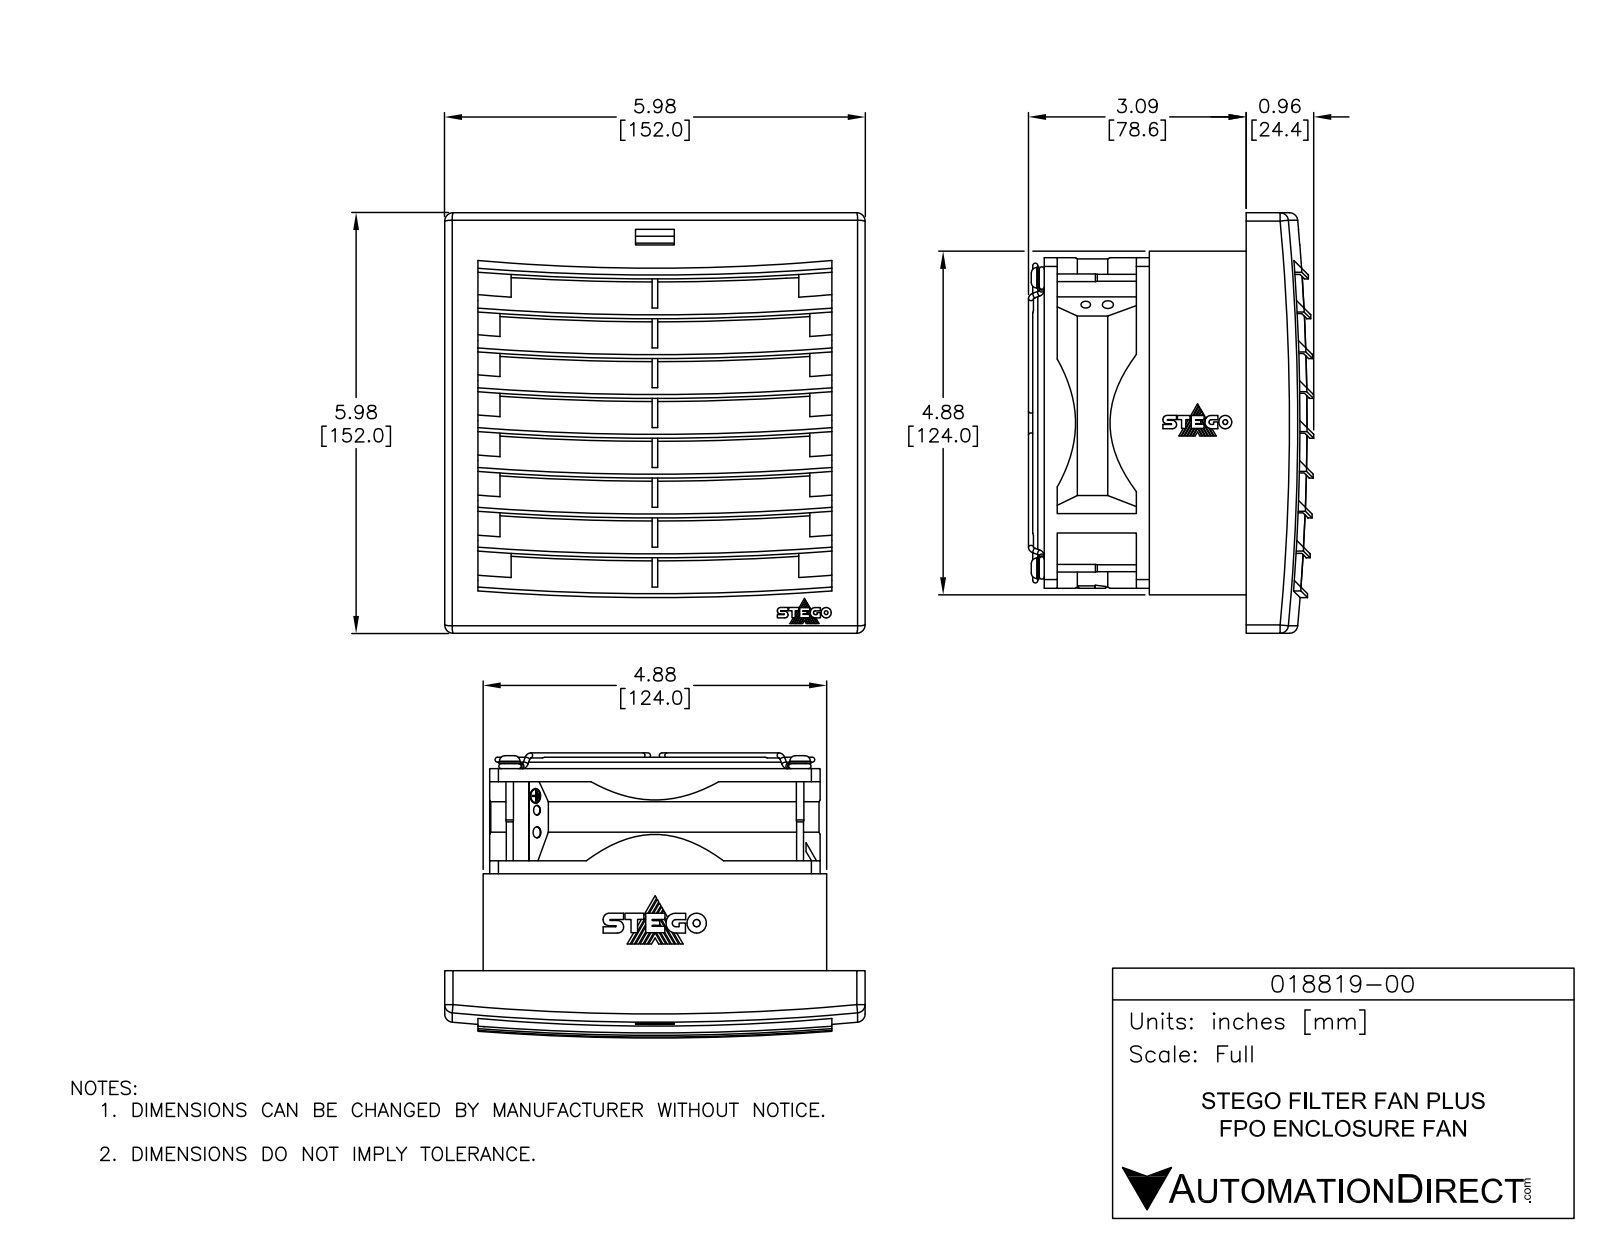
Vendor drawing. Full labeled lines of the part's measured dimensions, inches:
Part name (STEP PRODUCT): 018819-00
STEP written by: SolidWorks 2018 (AUTOMOTIVE_DESIGN)
Units: inches
Bodies: 1 solid, 544 faces (329 planar, 207 cylindrical, 8 other)
Overall size (bounding box): 5.985 × 5.984 × 4.094
Volume: 32.77 in³ · Surface area: 359.5 in²
Round holes (diameter × count): ⌀0.256 ×4, ⌀0.98 ×1, ⌀1.66 ×1, ⌀2.34 ×1, ⌀3.02 ×1, ⌀3.253 ×1, ⌀3.78 ×1, ⌀4.15 ×1
Round bosses / shafts (diameter × count): ⌀4.346 ×1, ⌀3.49 ×1, ⌀3.178 ×1, ⌀2.712 ×1, ⌀2.498 ×1, ⌀1.817 ×1, ⌀1.323 ×1, ⌀1.137 ×1
Partial cylindrical surfaces — rounded edges, fillets, slot ends (radius × count): R13.757 ×16, R1.852 ×5, R0.118 ×4, R0.142 ×4, R0.519 ×1, R0.849 ×1, R0.967 ×1, R1.238 ×1
Main face-to-face distances: 0.059, 0.426, 0.122, 4.76, 0.852, 0.079, 0.135, 0.269, 0.485, 0.367
Hole centre spacings: 3.007, 4.252, 6.013
